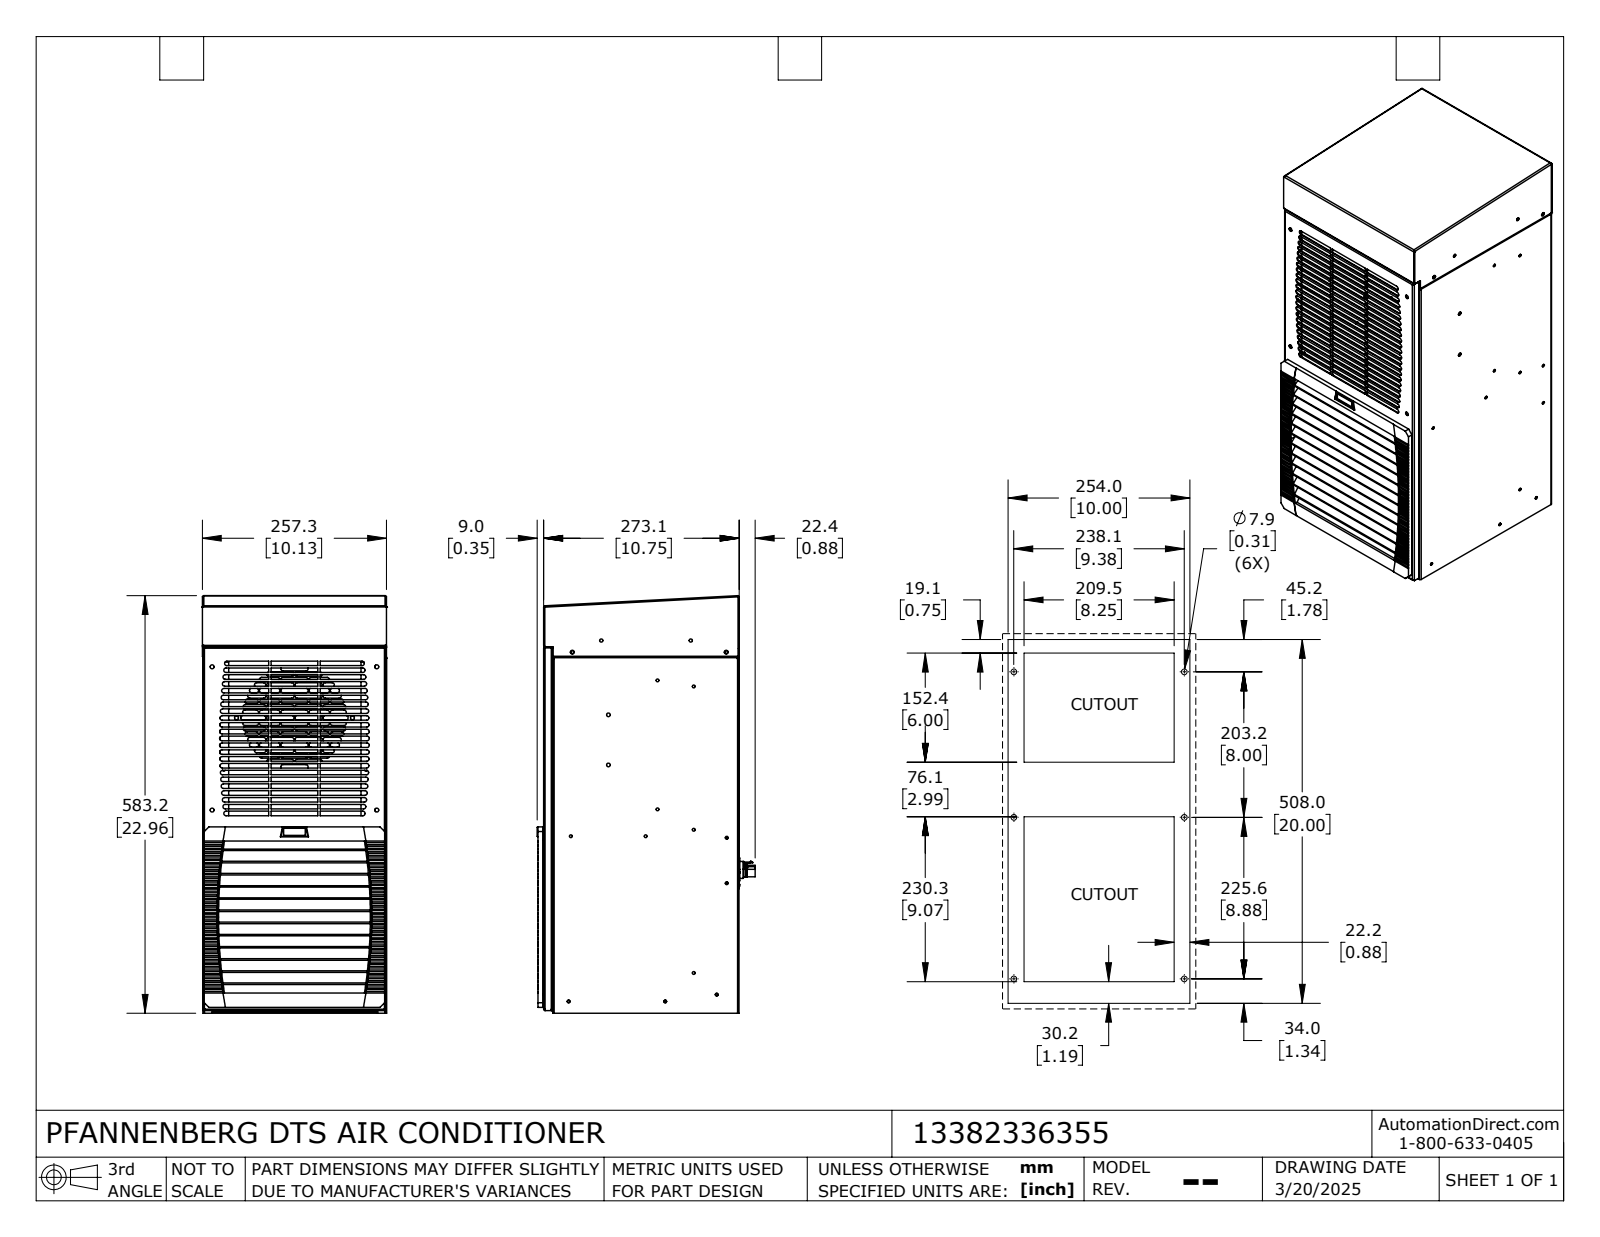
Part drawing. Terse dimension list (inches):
name: 13382336355_Default
written by: SolidWorks 2024 (CONFIG_CONTROL_DESIGN)
unit: in
bodies: 10 solids, 2397 faces (1380 planar, 906 cylindrical, 111 other)
size: 22.962 × 11.99 × 10.135
volume: 112.5 in³; area: 2 736 in²
holes: 12× ⌀0.156, 12× ⌀0.157, 12× ⌀0.217, 8× ⌀0.187, 6× ⌀0.165, 5× ⌀0.169, 5× ⌀0.209, 4× ⌀0.149, 4× ⌀0.281, 4× ⌀0.313, 4× ⌀0.394, 3× ⌀0.129
bosses: 4× ⌀0.079, 1× ⌀1.378, 1× ⌀1.102, 1× ⌀0.945, 1× ⌀0.906, 1× ⌀0.56, 1× ⌀0.475, 1× ⌀0.475
rounds: 186× R0.125, 43× R0.118, 32× R0.031, 32× R0.076, 24× R0.049, 10× R0.031, 10× R0.076, 8× R0.079
face distances: 0.045, 0.045, 10.006, 10.051, 10.05, 10.096, 10.711, 0.039, 10.045, 0.473
hole spacings: 4.921, 0.294, 2.5, 7.874, 9.195, 0.022, 0.244, 7.767
